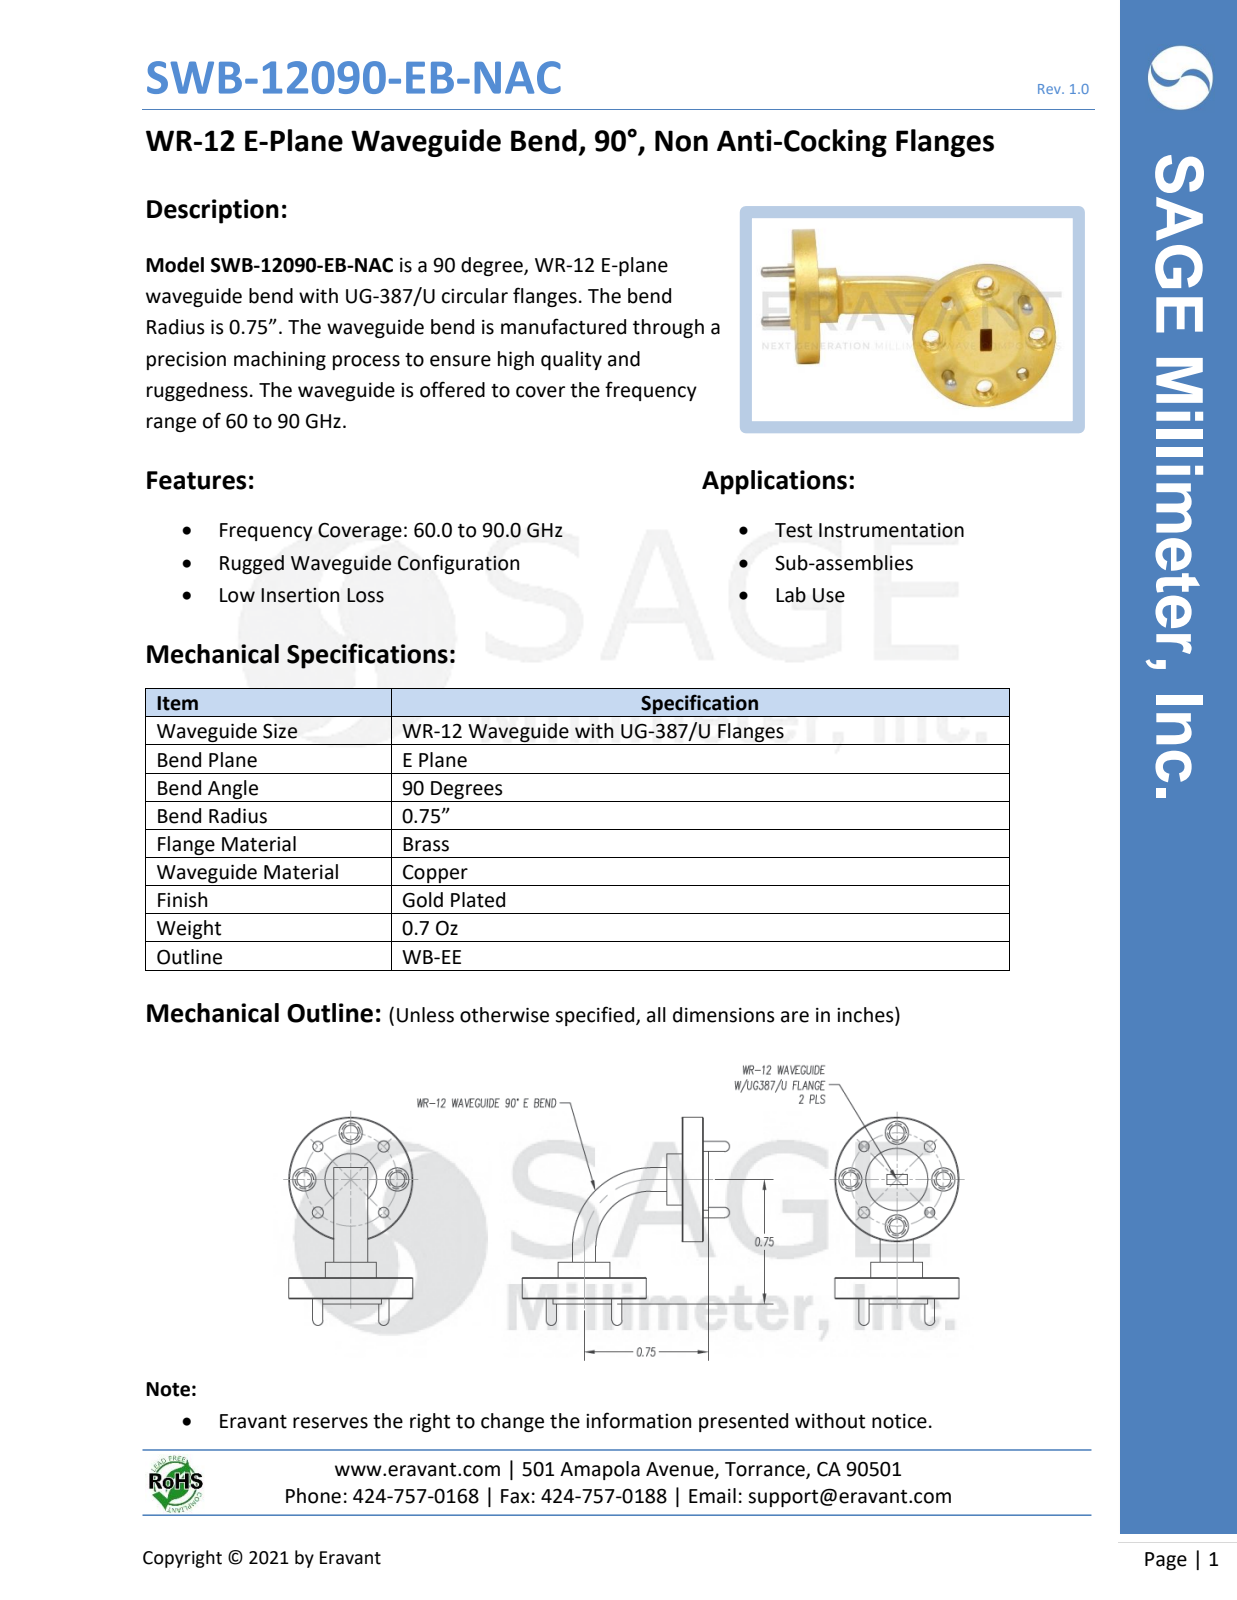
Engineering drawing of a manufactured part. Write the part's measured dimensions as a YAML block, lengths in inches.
part_name: "WB-EE"
step_written_by: "SolidWorks 2013 (CONFIG_CONTROL_DESIGN)"
units: inches
bodies: {solids: 5, faces: 152, planar: 40, cylindrical: 72, other: 40}
overall_size: [1.278, 1.278, 0.75]
volume: 0.147
surface_area: 4.127
round_holes:
  - {diameter: 0.089, count: 8}
  - {diameter: 0.14, count: 8}
  - {diameter: 0.06, count: 4}
  - {diameter: 0.067, count: 4}
round_bosses_or_shafts:
  - {diameter: 0.063, count: 4}
  - {diameter: 0.75, count: 2}
  - {diameter: 0.35, count: 2}
  - {diameter: 0.375, count: 1}
  - {diameter: 0.375, count: 1}
partial_cylinders:
  - {radius: 0.429, count: 1}
  - {radius: 0.469, count: 1}
  - {radius: 0.531, count: 1}
  - {radius: 0.571, count: 1}
face_to_face_distances: [0.13, 0.03, 0.16, 0.26, 0.23, 0.1, 0.202, 0.05, 0.02, 0.11]
hole_center_spacings: [0.215, 0.398, 0.52, 0.563, 0.519, 0.398, 0.562, 0.216]
